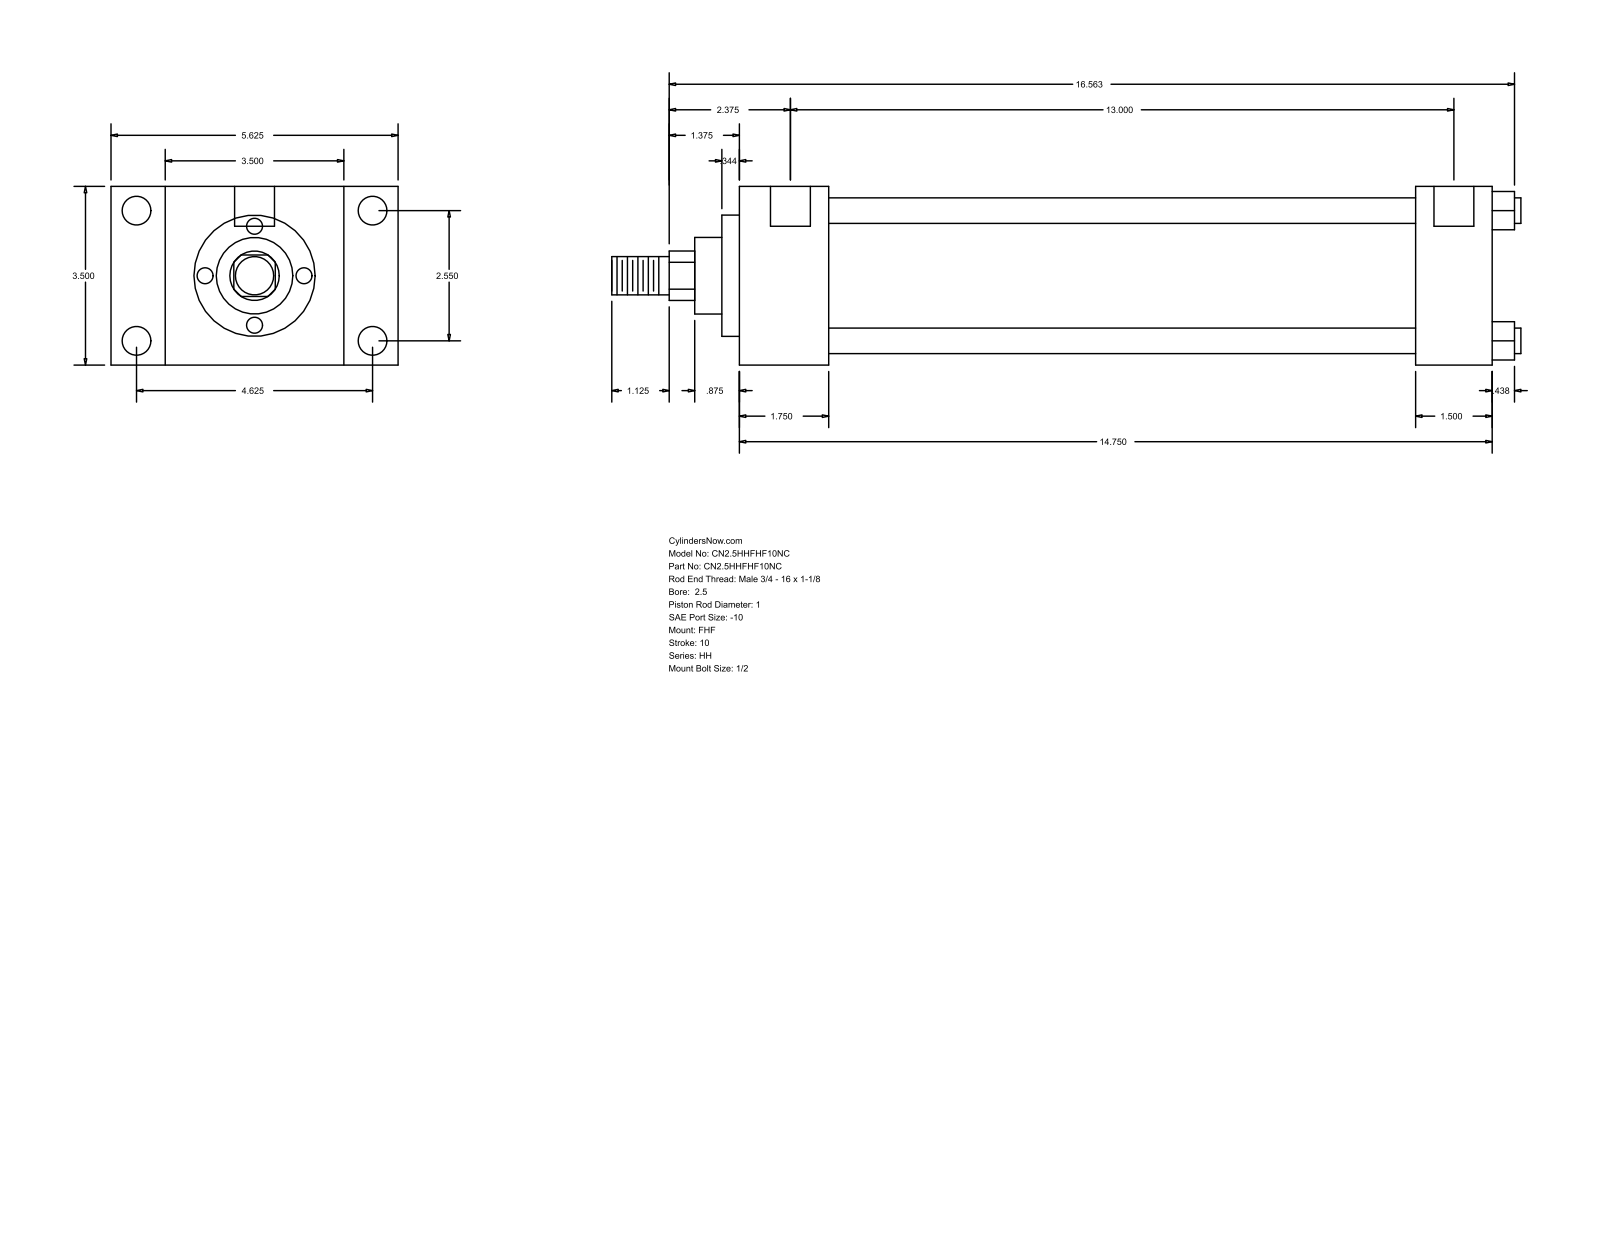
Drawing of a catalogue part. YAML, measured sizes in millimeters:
part_name: "HH_FHF__0250_1"
step_written_by: "GSSL Pune (CONFIG_CONTROL_DESIGN)"
units: millimeters
bodies: {solids: 0, faces: 90, planar: 61, cylindrical: 29, other: 0}
overall_size: [452.44, 142.88, 88.9]
round_holes:
  - {diameter: 5.56, count: 4}
  - {diameter: 14.3, count: 4}
  - {diameter: 19.84, count: 2}
round_bosses_or_shafts:
  - {diameter: 12.7, count: 4}
  - {diameter: 73.03, count: 1}
  - {diameter: 60.33, count: 1}
  - {diameter: 38.1, count: 1}
  - {diameter: 25.4, count: 1}
  - {diameter: 19.05, count: 1}
partial_cylinders:
  - {radius: 12.29, count: 1}
face_to_face_distances: [88.9, 44.46, 26.99, 115.89, 374.65, 330.19, 142.88, 336.56, 292.1, 38.09]
hole_center_spacings: [1.59, 64.76, 117.48, 134.15, 331.78, 333.37, 330.19]
